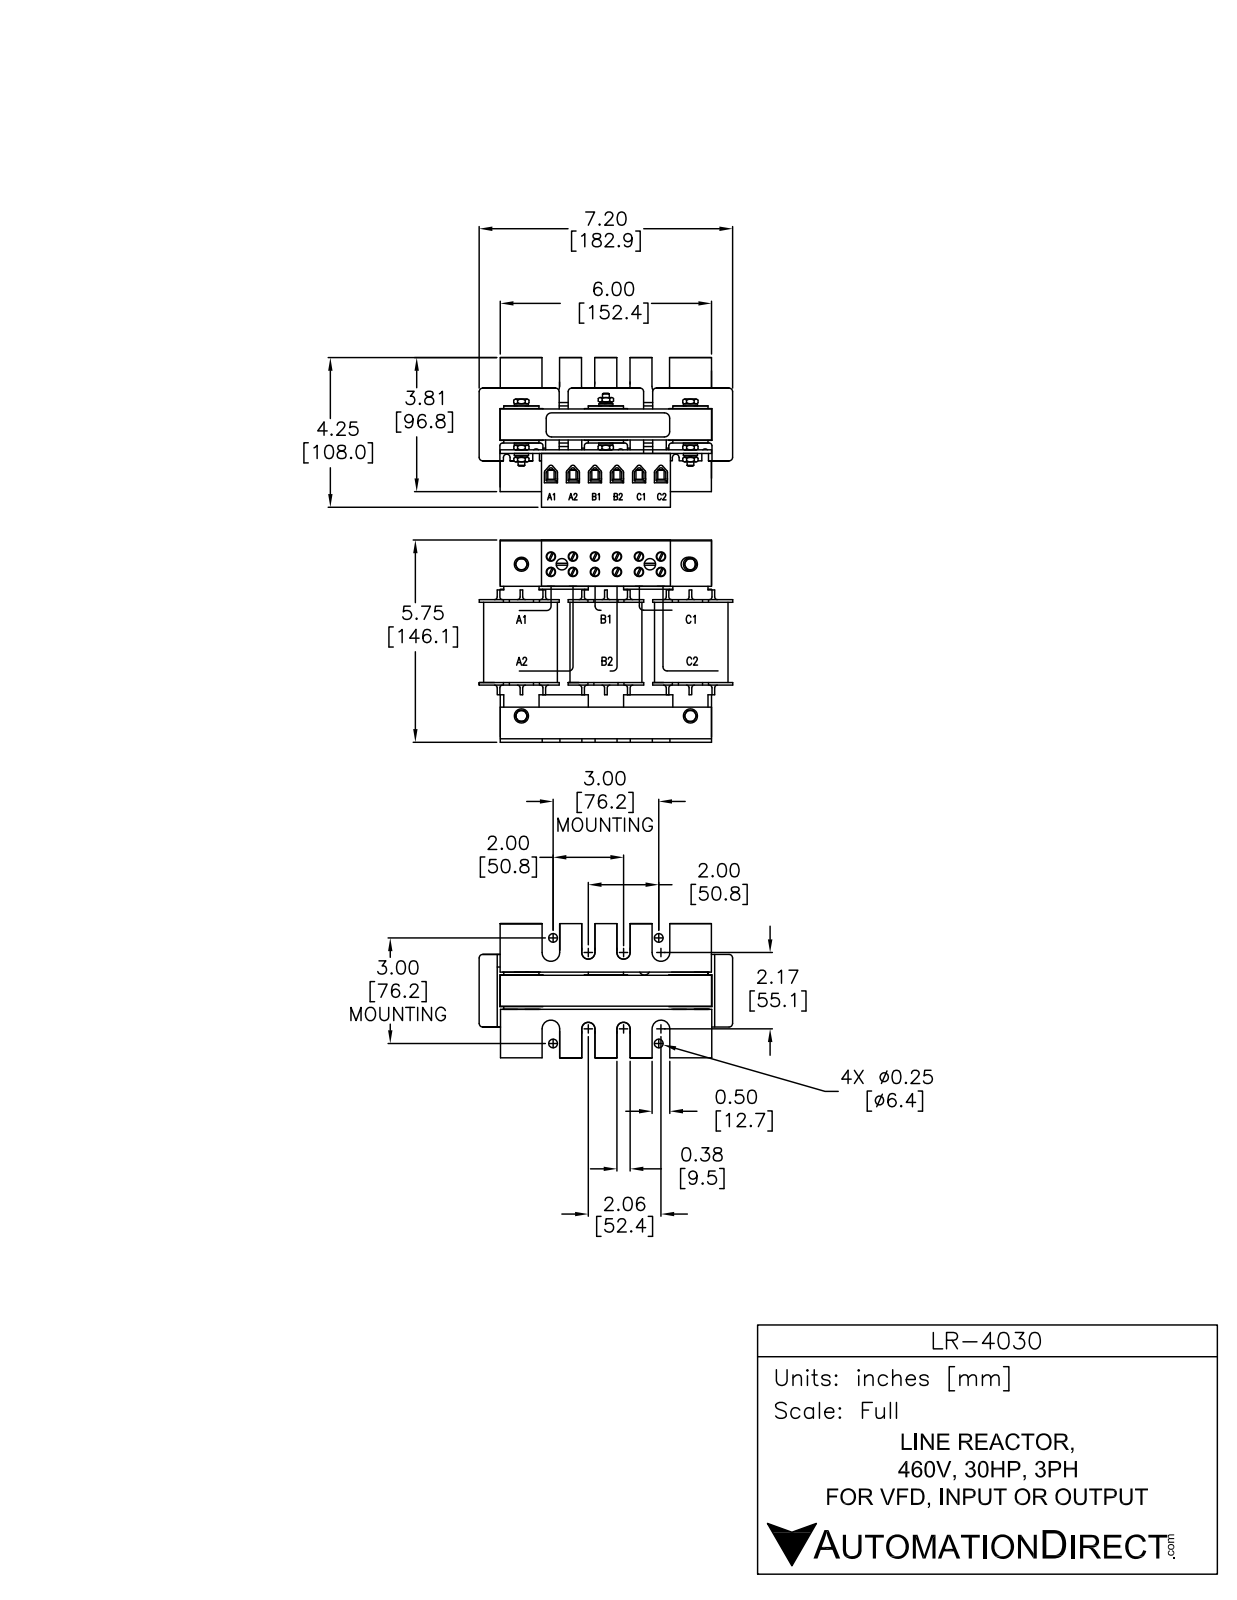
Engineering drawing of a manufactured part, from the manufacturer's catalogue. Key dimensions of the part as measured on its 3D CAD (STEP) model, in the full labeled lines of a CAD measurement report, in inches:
Part name (STEP PRODUCT): LR-4030
STEP written by: SolidWorks 2011 (AUTOMOTIVE_DESIGN)
Units: inches
Bodies: 34 solids, 1041 faces (767 planar, 242 cylindrical, 32 other)
Overall size (bounding box): 7.008 × 5.619 × 3.907
Volume: 51.71 in³ · Surface area: 302.9 in²
Round holes (diameter × count): ⌀0.276 ×12, ⌀0.305 ×5
Round bosses / shafts (diameter × count): ⌀0.472 ×5, ⌀0.413 ×5, ⌀0.305 ×2, ⌀0.183 ×2, ⌀0.184 ×1, ⌀0.183 ×1, ⌀0.183 ×1
Partial cylindrical surfaces — rounded edges, fillets, slot ends (radius × count): R0.106 ×24, R0.197 ×12, R0.276 ×12, R0.089 ×6, R0.059 ×4, R0.177 ×4, R0.246 ×4, R0.128 ×2
Main face-to-face distances: 0.079, 0.364, 2.441, 1.329, 1.407, 0.108, 0.344, 0.266, 0.443, 0.187
Hole centre spacings: 0.63, 1.26, 0.376, 0.394, 0.77, 0.96, 0.981, 1.335
